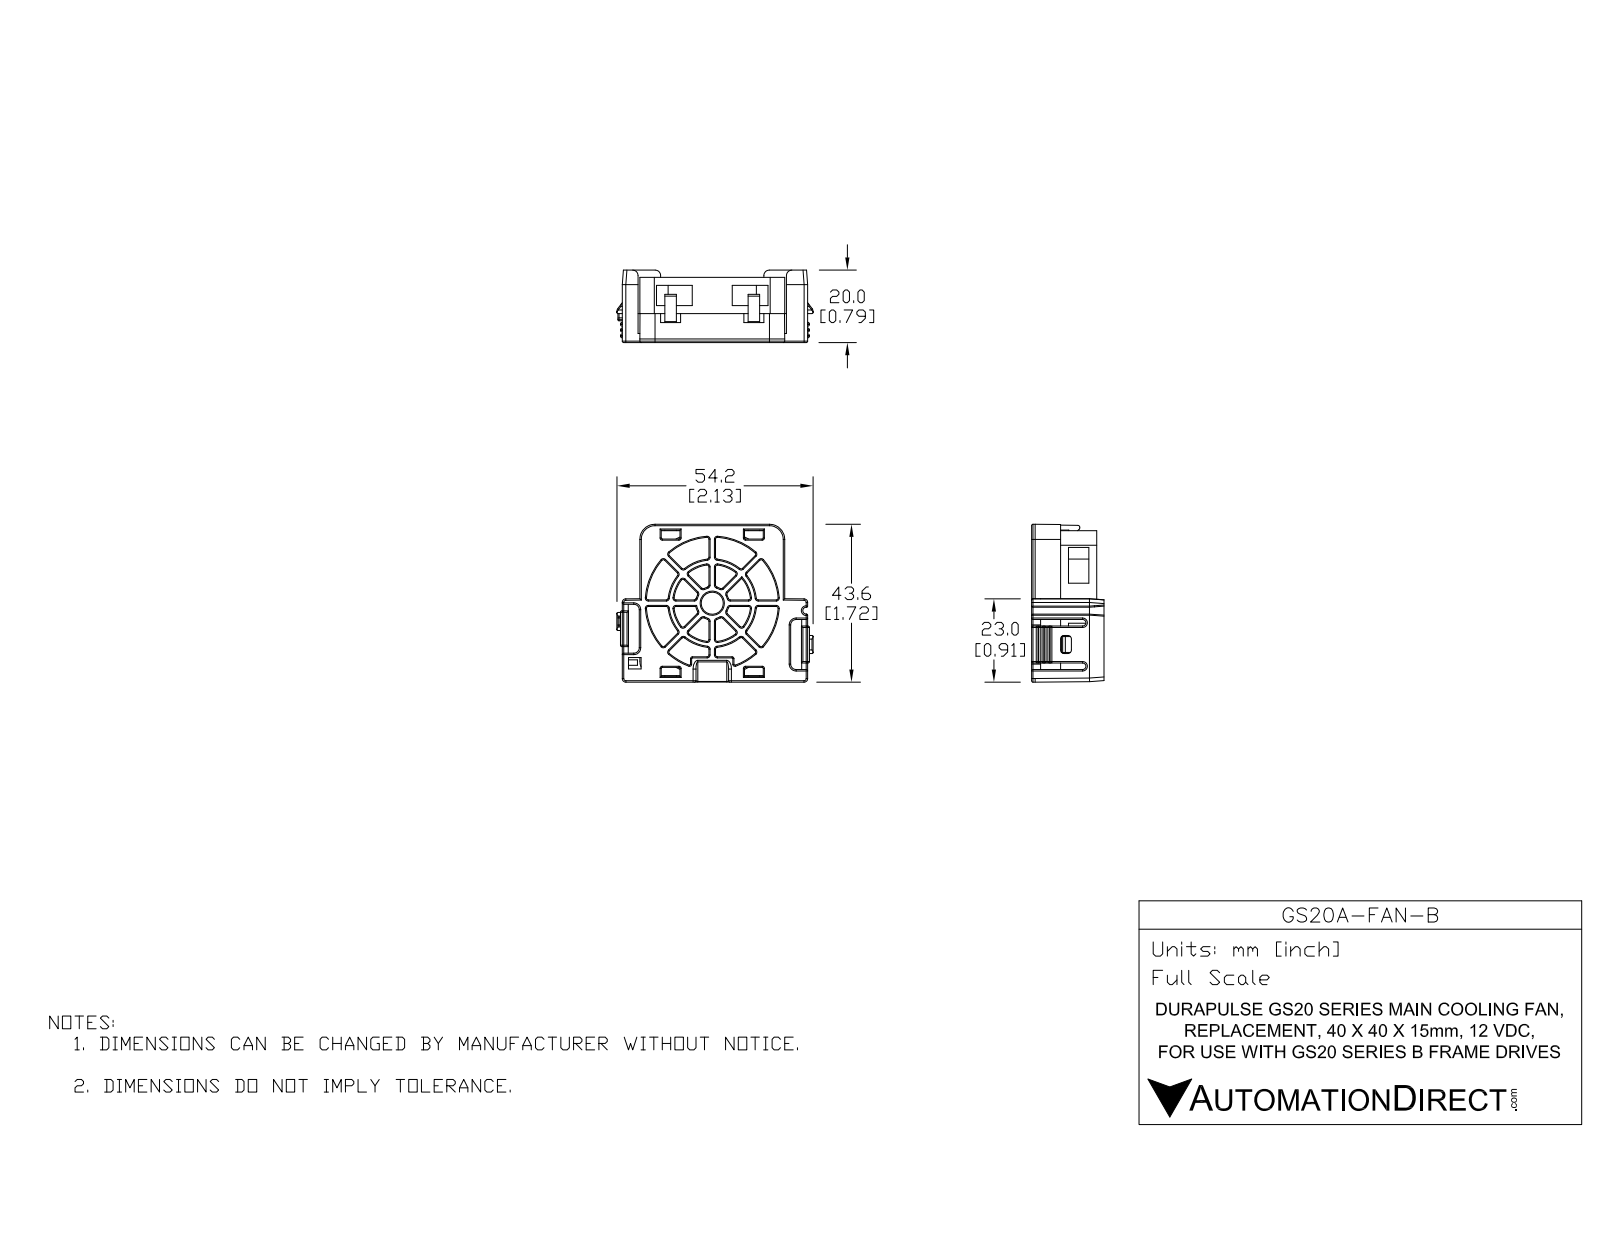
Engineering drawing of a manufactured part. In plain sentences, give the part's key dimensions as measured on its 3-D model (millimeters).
The part is named "GS20A-FAN-B". Its 3-D file was written by "SolidWorks 2017 (AUTOMOTIVE_DESIGN)". It is 3 solids with 927 faces: 311 planar, 360 cylindrical and 256 other. Overall it measures 54.2 by 43.6 by 20 millimeters. Its volume is 12 900 cubic millimeters and its surface area 15 230 square millimeters. Round holes: 4 of diameter 3.2, 1 of diameter 6.1. Round bosses or shafts: 1 of diameter 23. Partial cylindrical surfaces (rounded edges, fillets, slot ends): 82 of radius 0.5, 56 of radius 0.3, 39 of radius 0.4, 19 of radius 1, 10 of radius 1.5, 4 of radius 0.9, 4 of radius 1.2, 4 of radius 4. The main face-to-face distances are 8, 2.5, 5.5, 15.5, 18, 10, 0.8, 39.1, 40, 38.3. The hole center spacings are 22.6, 32, 45.2.
